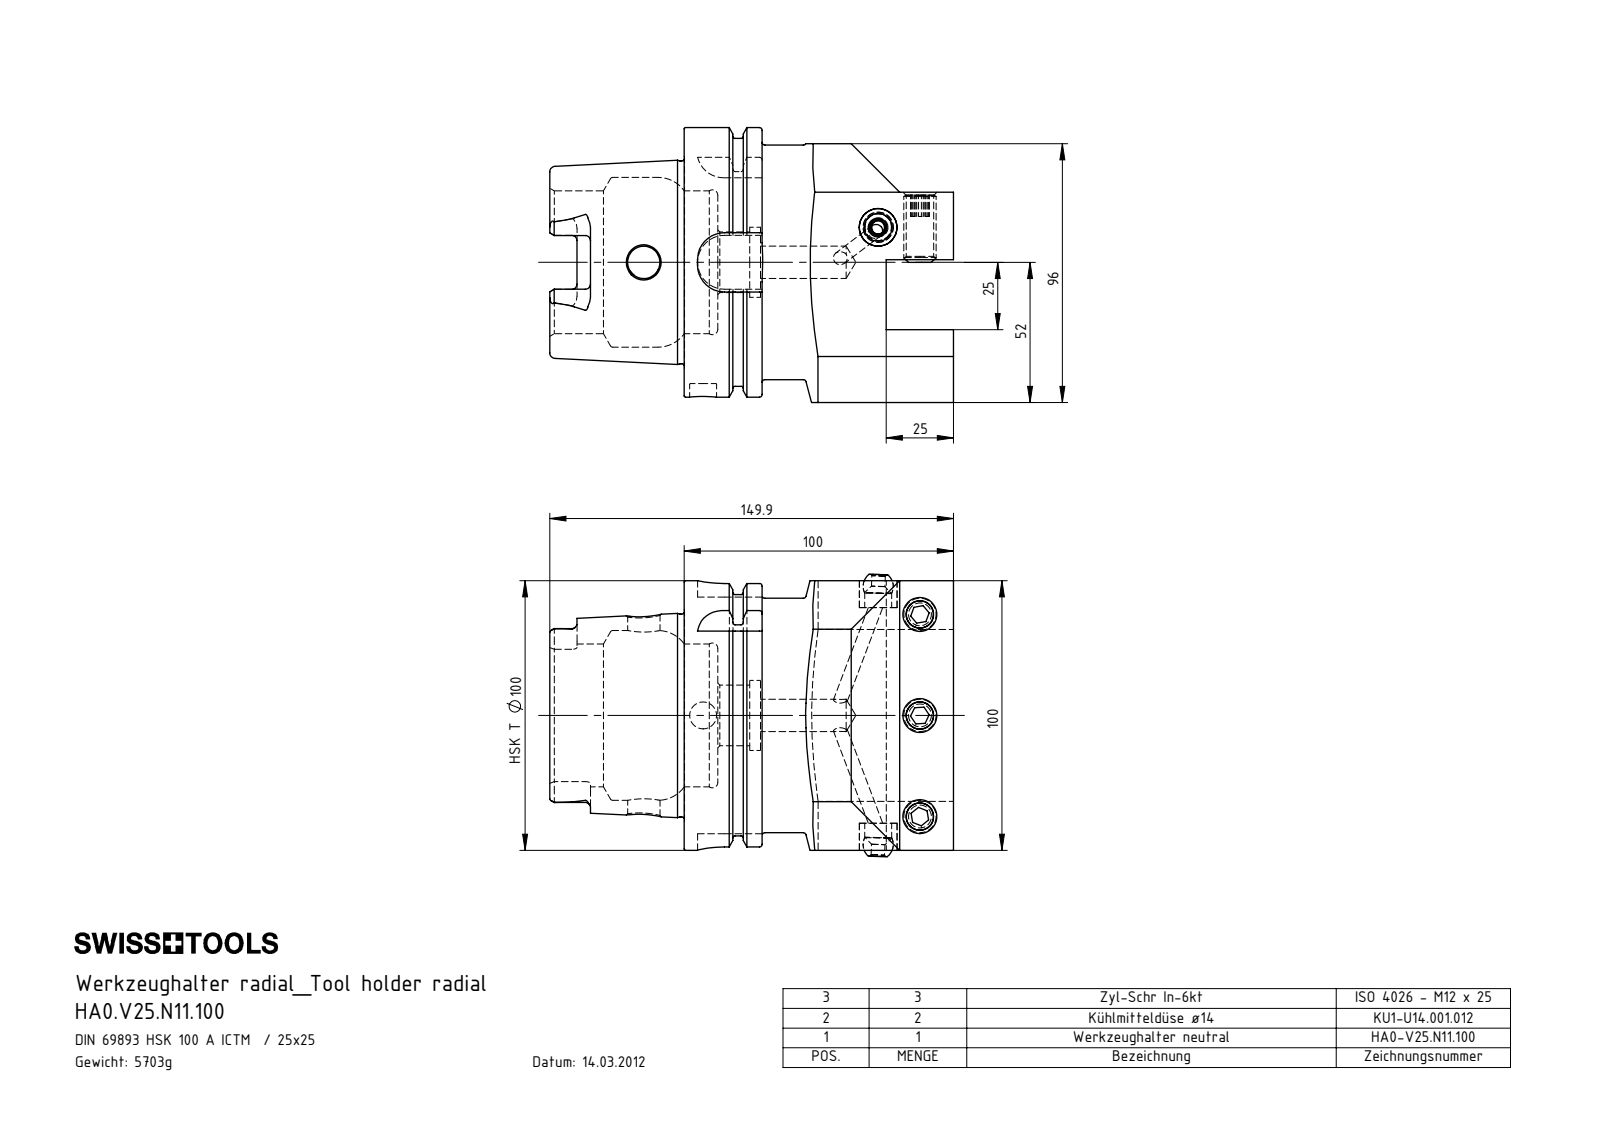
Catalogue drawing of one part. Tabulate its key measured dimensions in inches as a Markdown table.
| quantity | value |
| --- | --- |
| part name | HA0.V25.N11.100; ISO 4026 - M12 x 25_Default; KU1-U14.001.012; KU1-U14.001.012_2 (+2 more) |
| STEP written by | SolidWorks 2011 (CONFIG_CONTROL_DESIGN) |
| units | inches |
| bodies | 8 solids, 273 faces (85 planar, 82 cylindrical, 106 other) |
| overall size | 5.902 × 4.126 × 4.016 |
| volume | 44.4 in³ |
| surface area | 143.1 in² |
| round holes (diameter × count) | 0.197 × 4, 0.402 × 3, 0.394 × 2, 0.472 × 2, 0.551 × 1, 0.886 × 1, 1.024 × 1, 2.087 × 1, 2.48 × 1 |
| round bosses / shafts (diameter × count) | 0.472 × 3, 3.937 × 1, 3.62 × 1, 3.425 × 1, 2.963 × 1 |
| partial cylindrical surfaces (radius × count) | 0.075 × 6, 0.192 × 4, 0.394 × 4, 2.402 × 1 |
| main face-to-face distances | 3.937, 0.984, 1.063, 2.953, 1.024, 2.087, 3.071, 2.008, 0.49, 2.463 |
| hole center spacings | 1.476, 3.496, 2.953, 3.169, 3.463 |
